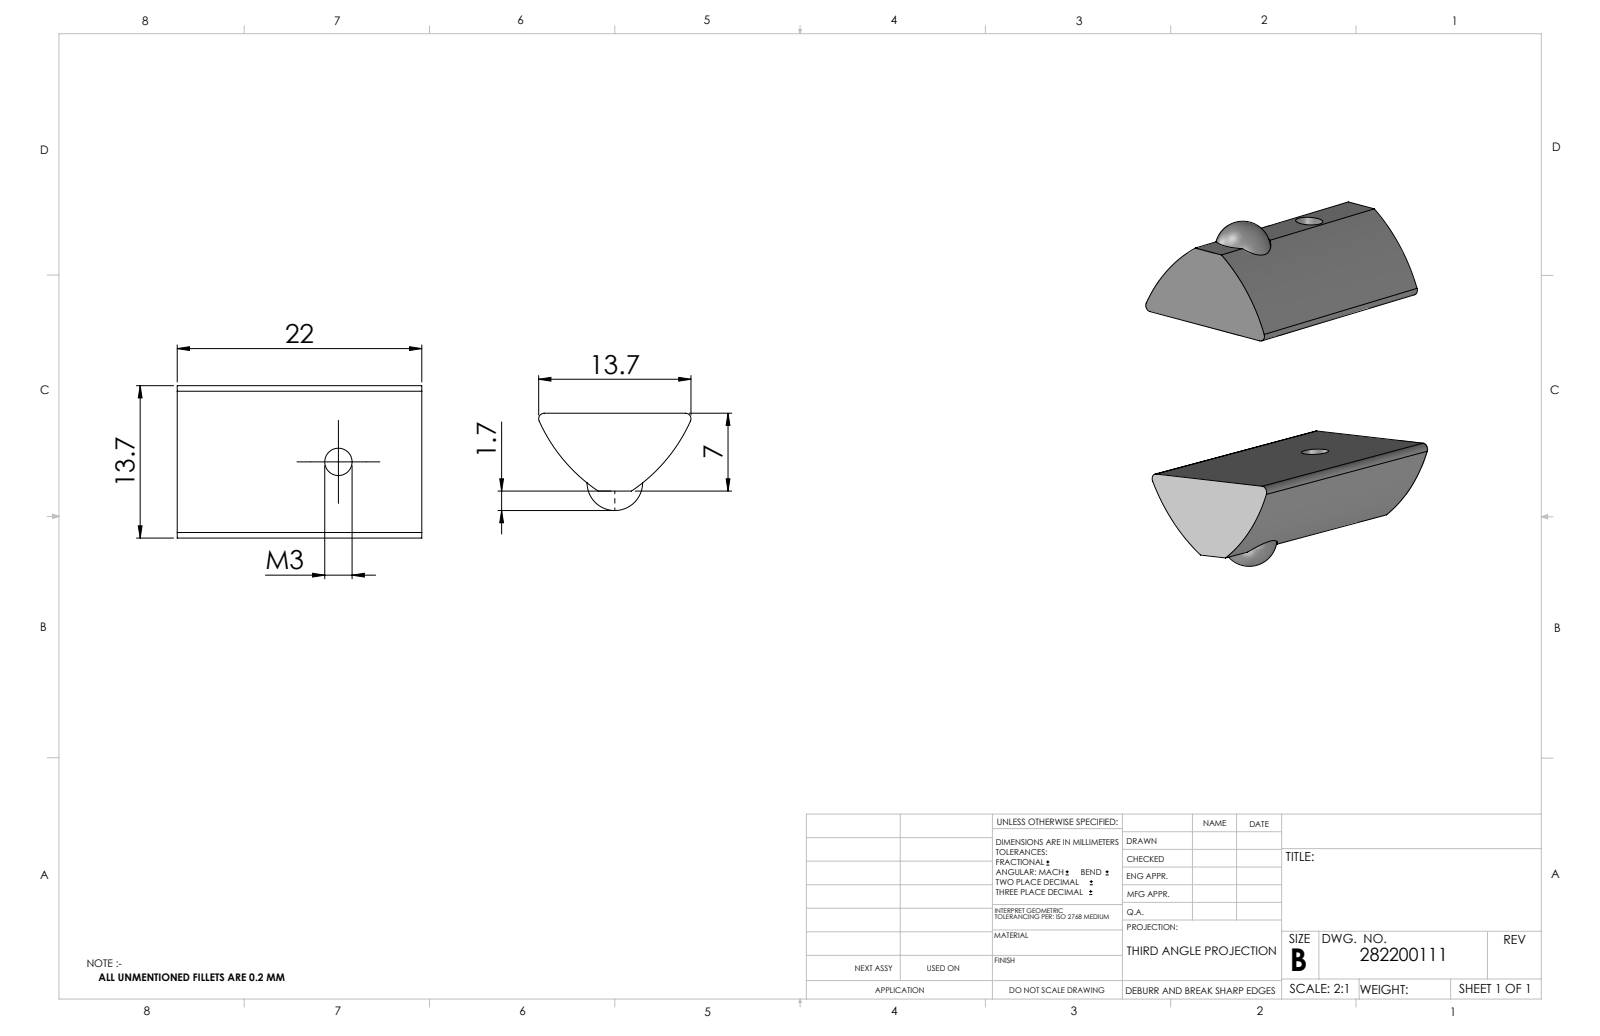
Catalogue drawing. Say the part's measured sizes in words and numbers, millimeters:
The part is named "282200111". Its 3-D file was written by "SolidWorks 2014 (CONFIG_CONTROL_DESIGN)". It is 1 solid with 15 faces: 6 planar, 8 cylindrical and 1 other. Overall it measures 22 by 13.7 by 8.74 millimeters. Its volume is 1 486 cubic millimeters and its surface area 963 square millimeters. Round holes: 1 of diameter 2.46, 1 of diameter 5. Partial cylindrical surfaces (rounded edges, fillets, slot ends): 2 of radius 0.5, 2 of radius 15. The main face-to-face distances are 22, 7, 0.75, 6.25. The hole center spacings are 9.5.
